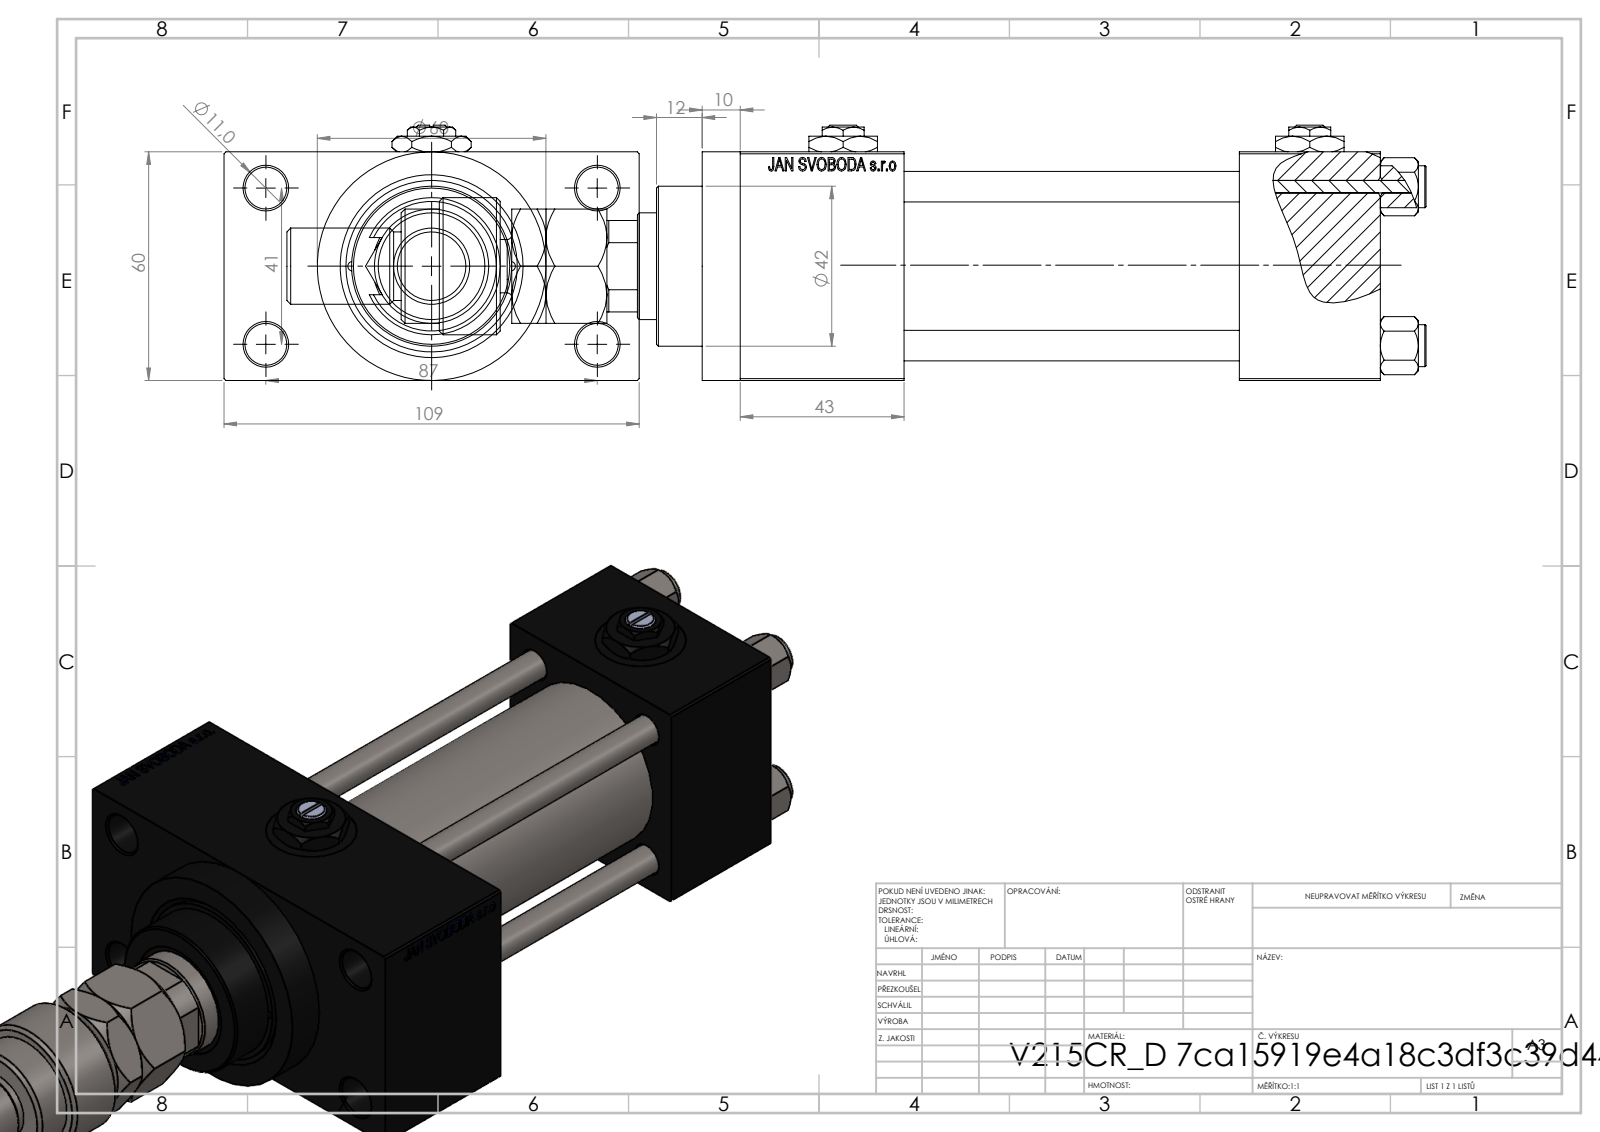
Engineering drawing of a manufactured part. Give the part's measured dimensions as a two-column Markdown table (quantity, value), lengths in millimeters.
| quantity | value |
| --- | --- |
| part name | V215CR_D_Body; Zatka_pro_OIL_PORT; NUT_M5_D; V215CR_D_TYCINKA (+4 more) |
| STEP written by | SolidWorks 2019 (CONFIG_CONTROL_DESIGN) |
| units | millimeters |
| bodies | 15 solids, 1300 faces (578 planar, 116 cylindrical, 606 other) |
| overall size | 299 × 109 × 67 |
| volume | 612 061 mm³ |
| surface area | 158 724 mm² |
| round holes (diameter × count) | 8 × 4, 11 × 4, 16.66 × 4, 24 × 4, 7 × 3, 2.5 × 2, 18.5 × 1, 28 × 1, 31 × 1, 40 × 1, 45 × 1 |
| round bosses / shafts (diameter × count) | 11 × 4, 60 × 1, 46 × 1, 42 × 1, 36 × 1, 30 × 1, 22 × 1, 20 × 1 |
| partial cylindrical surfaces (radius × count) | 7.5 × 1, 12 × 1, 13.5 × 1 |
| main face-to-face distances | 60, 88, 24.5, 84.5, 37, 125, 43, 168, 131, 109 |
| hole center spacings | 20.85, 22.65, 29.49, 30.62, 41.7, 46.53, 47.15, 48.09 |
